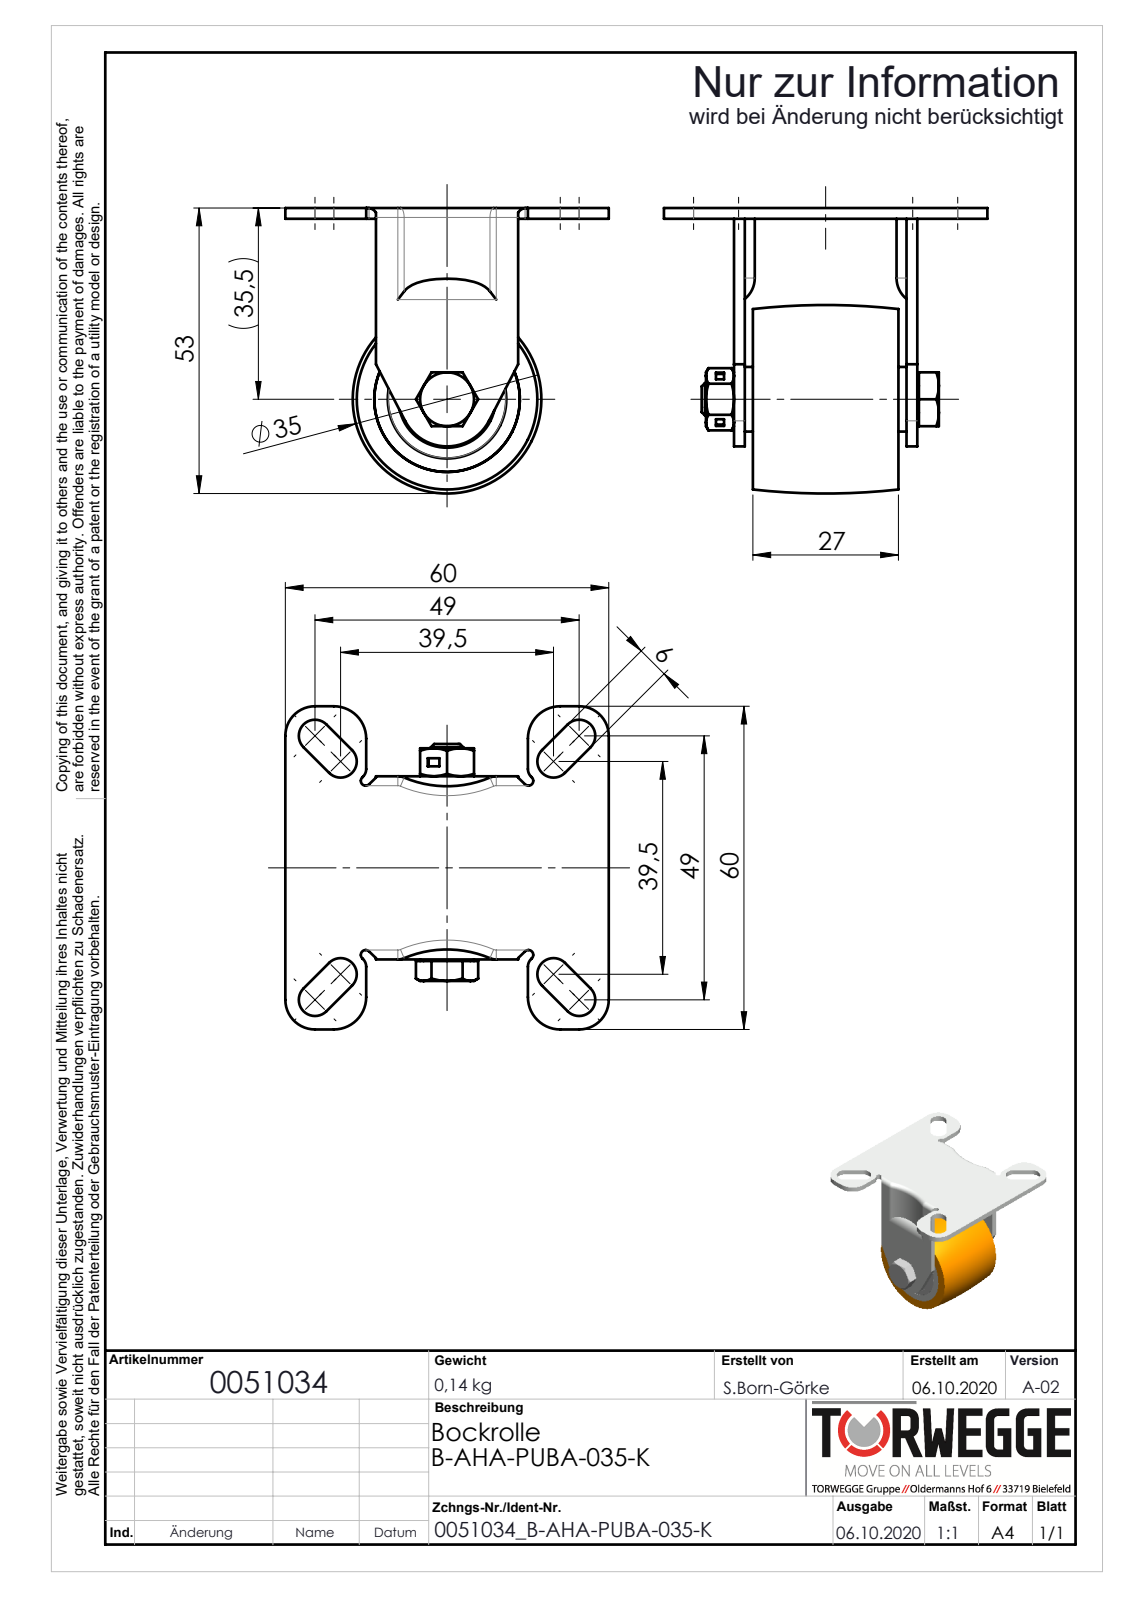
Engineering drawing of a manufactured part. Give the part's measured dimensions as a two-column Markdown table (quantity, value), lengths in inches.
| quantity | value |
| --- | --- |
| part name | 0051034 |
| STEP written by | SolidWorks 2018 (AUTOMOTIVE_DESIGN) |
| units | inches |
| bodies | 15 solids, 279 faces (98 planar, 106 cylindrical, 75 other) |
| overall size | 2.362 × 2.362 × 2.087 |
| volume | 1.804 in³ |
| surface area | 43.13 in² |
| round holes (diameter × count) | 0.197 × 1, 0.236 × 1, 0.244 × 1, 0.315 × 1, 0.472 × 1, 0.709 × 1, 1.063 × 1 |
| round bosses / shafts (diameter × count) | 0.866 × 1, 0.394 × 1 |
| partial cylindrical surfaces (radius × count) | 0.118 × 12, 0.035 × 4, 0.079 × 4, 0.217 × 4, 0.236 × 4, 0.805 × 4, 0.069 × 2, 0.197 × 2 |
| main face-to-face distances | 0.079, 1.26, 1.122, 1.201, 0.138, 0.059, 0.787, 1.181, 1.339, 1.063 |
